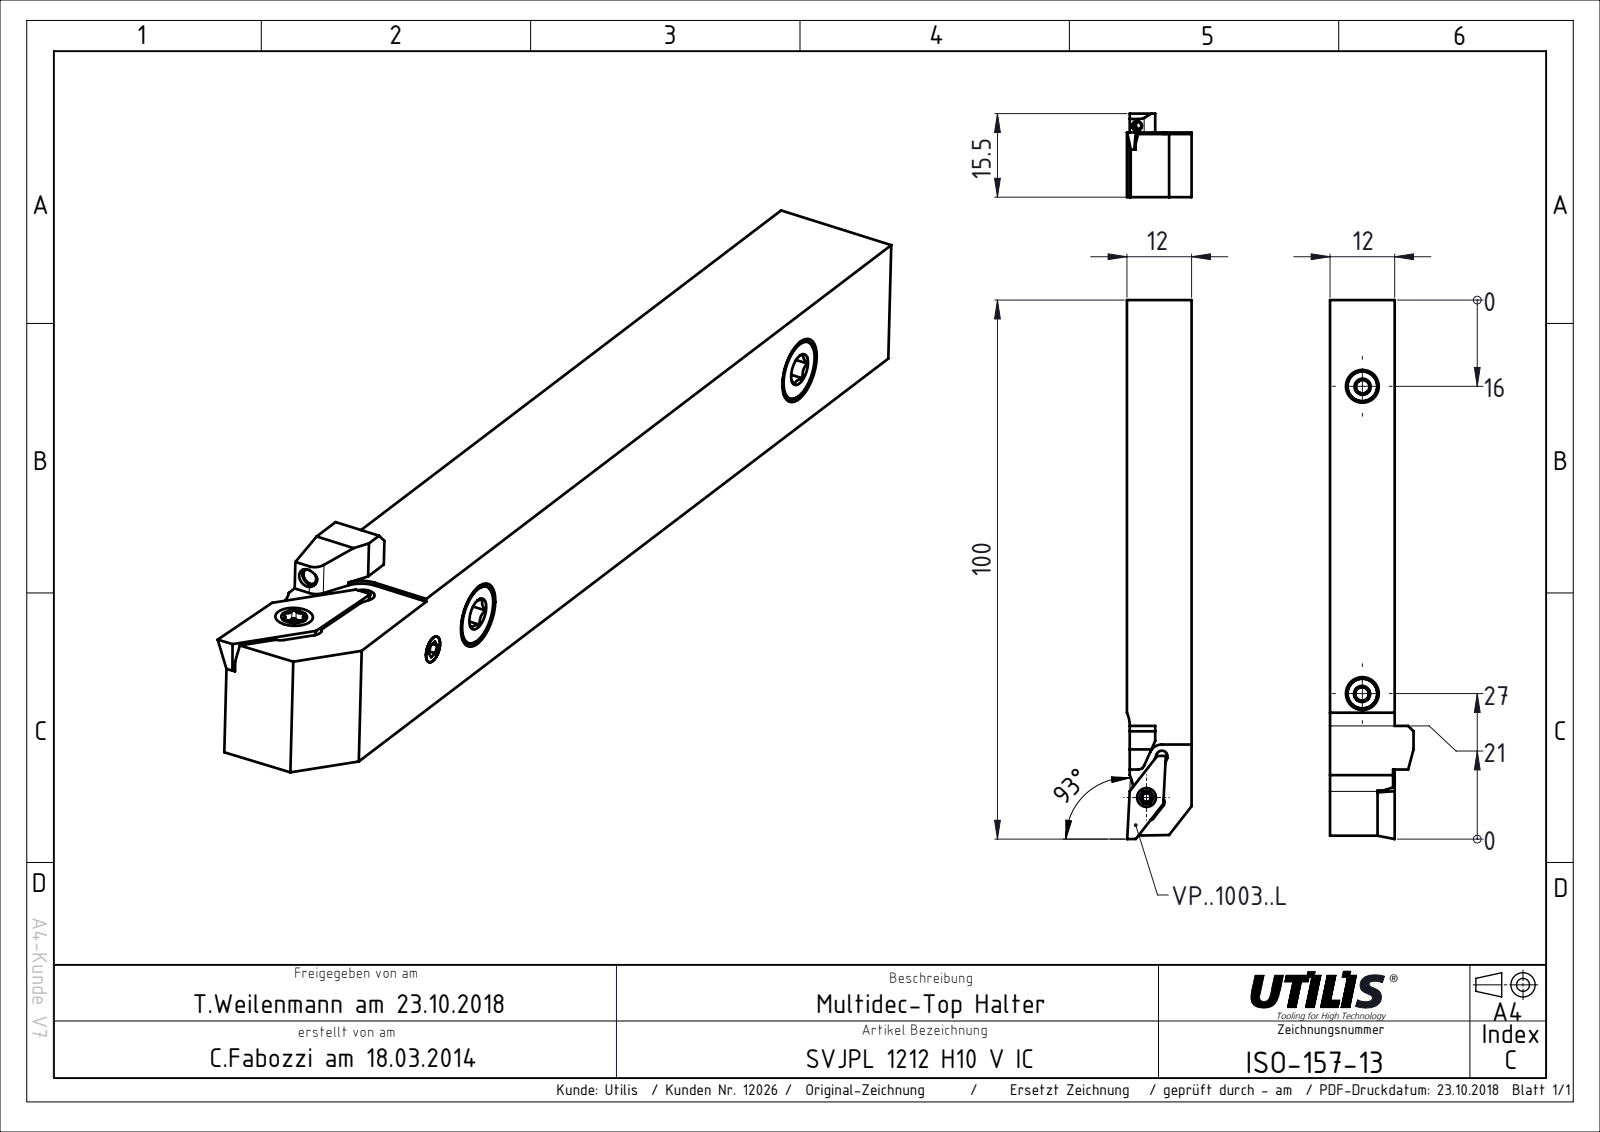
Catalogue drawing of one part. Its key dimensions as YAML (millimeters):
part_name: "ISO-157-13"
step_written_by: "SolidWorks 2015 (AUTOMOTIVE_DESIGN)"
units: millimeters
bodies: {solids: 1, faces: 57, planar: 50, cylindrical: 7, other: 0}
overall_size: [100, 15.5, 12.2]
volume: 14105
surface_area: 5168
partial_cylinders:
  - {radius: 1.05, count: 3}
  - {radius: 6.1, count: 2}
  - {radius: 2.3, count: 1}
face_to_face_distances: [12, 11.73, 11.7, 15.5, 3.8, 3.5, 8.82, 2.88, 3.18, 6.68]
